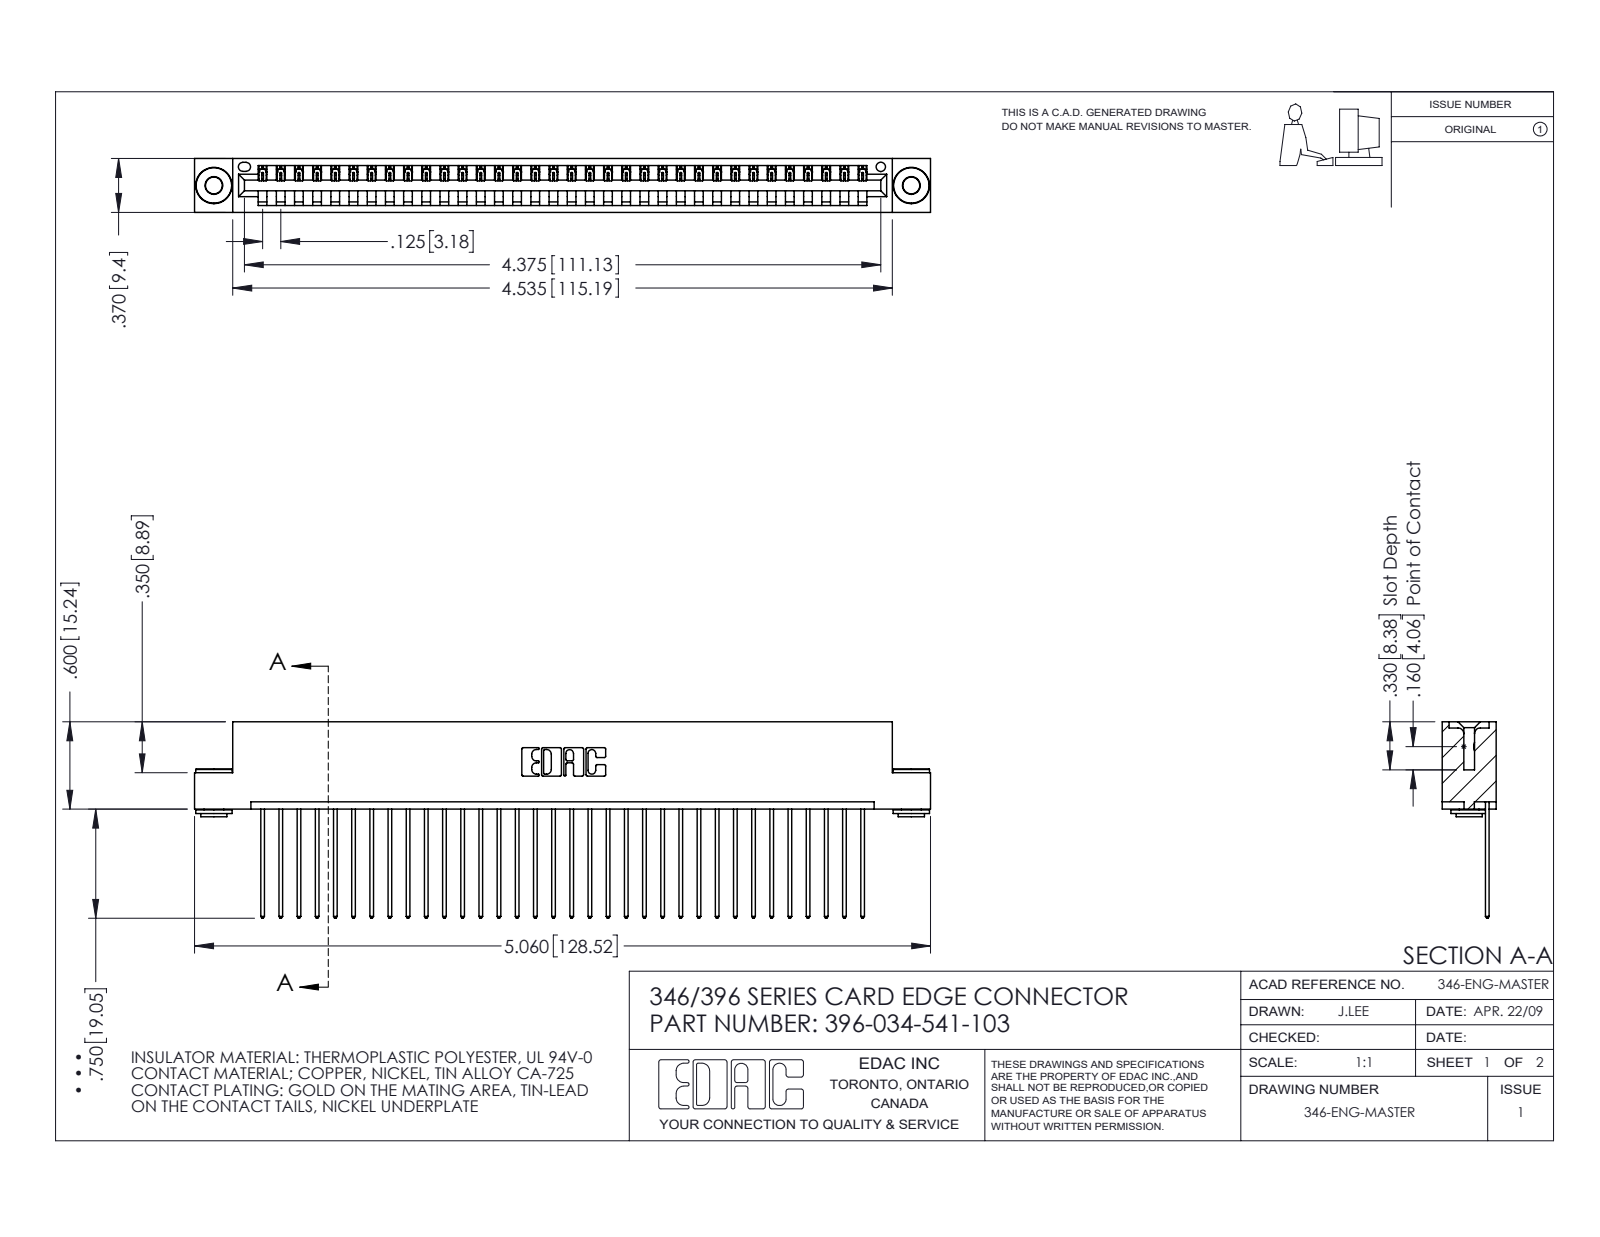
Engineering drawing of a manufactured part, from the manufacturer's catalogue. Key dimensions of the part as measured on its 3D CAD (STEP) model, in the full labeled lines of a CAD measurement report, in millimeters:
Part name (STEP PRODUCT): 345-250-002_345-250-002-102; 396-034-541-103; 345-292-001_345-293-141; 346 Part_Flush Mounting Lugs - 0.156 Dia-TH
STEP written by: SolidWorks 2016 (CONFIG_CONTROL_DESIGN)
Units: millimetres
Bodies: 37 solids, 2132 faces (1446 planar, 678 cylindrical, 8 other)
Overall size (bounding box): 128.5 × 34.3 × 9.4
Volume: 12 400 mm³ · Surface area: 16 280 mm²
Round holes (diameter × count): ⌀2.9 ×2, ⌀4 ×2, ⌀1.6 ×1
Round bosses / shafts (diameter × count): ⌀6.4 ×2, ⌀4.6 ×2, ⌀3.5 ×2
Partial cylindrical surfaces — rounded edges, fillets, slot ends (radius × count): R0.2 ×68, R0.3 ×68, R0.3 ×22, R0.2 ×6, R0.8 ×6, R0.7 ×3, R0.8 ×2, R1 ×2
Main face-to-face distances: 1.2, 8.2, 6.4, 9.4, 0.6, 1.8, 7.6, 3.8, 5.6, 2.5
Hole centre spacings: 6.2, 116.5, 121.8
